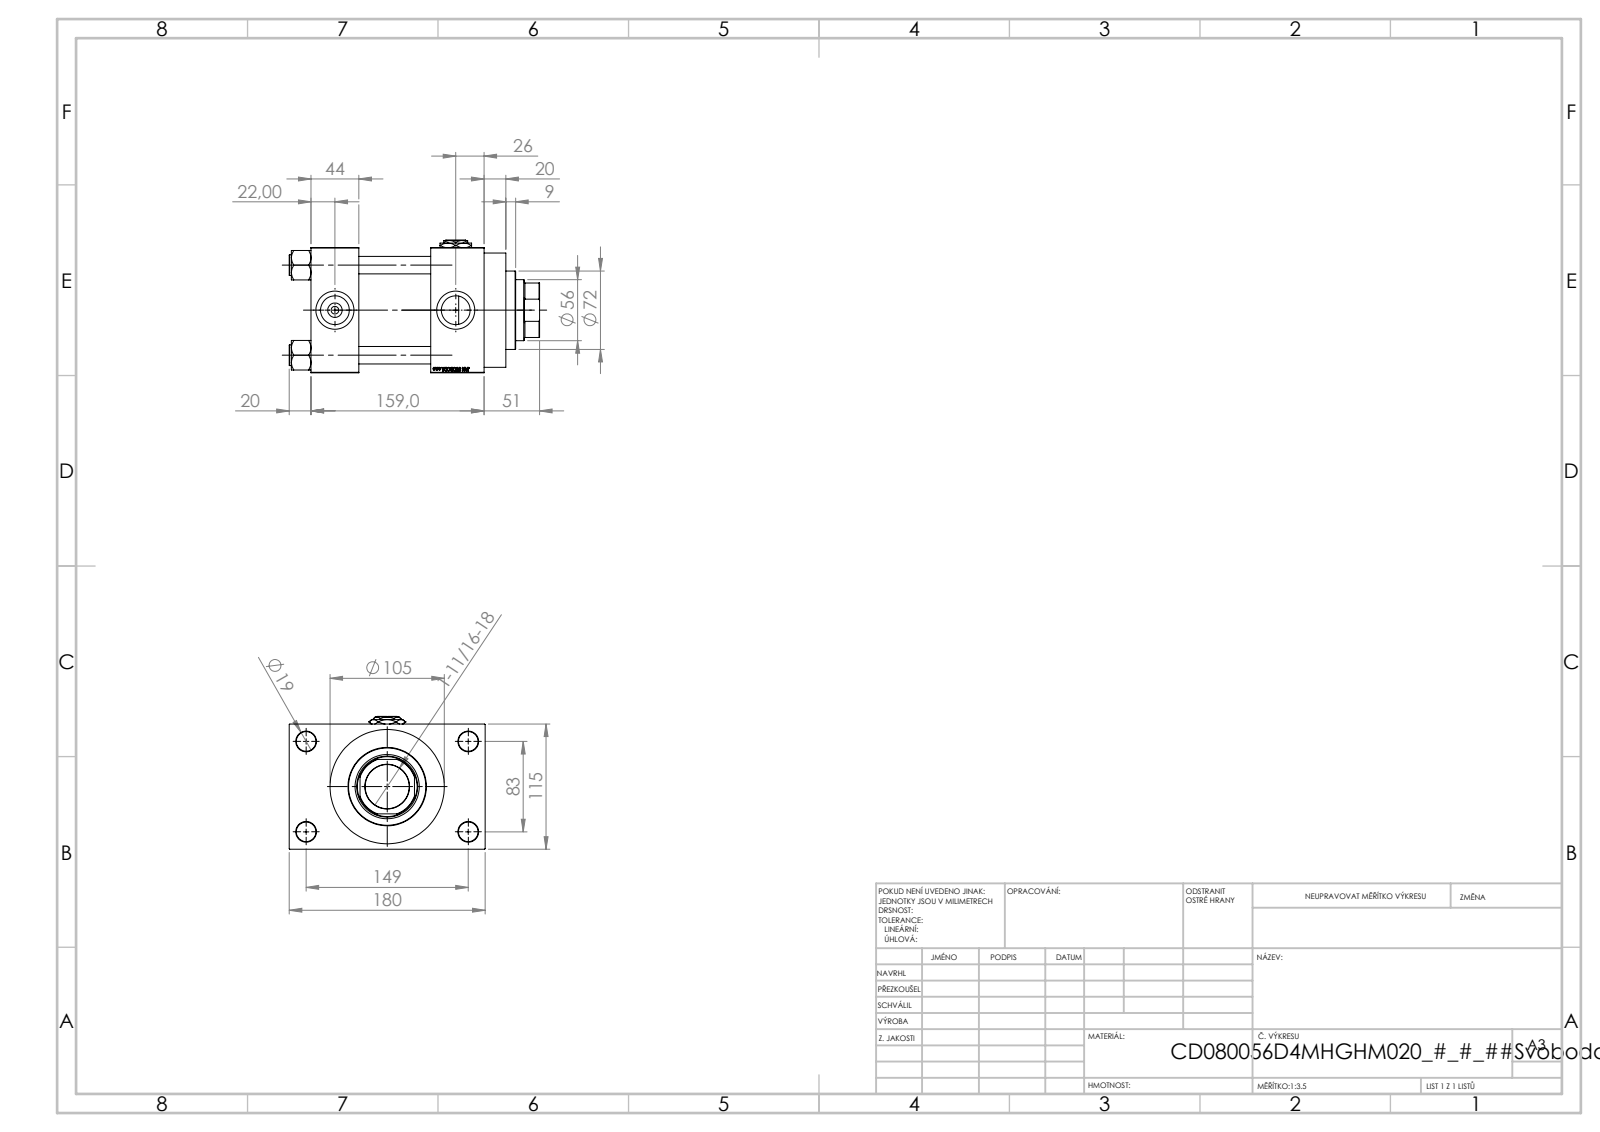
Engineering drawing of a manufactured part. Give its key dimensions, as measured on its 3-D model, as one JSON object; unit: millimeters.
{"part_name": "V215CD_NUT_M5_D; V215CD_D_TYCINKA; V215CD_VC_A; V215CD_VCP_D (+2 more)", "step_written_by": "SolidWorks 2019 (CONFIG_CONTROL_DESIGN)", "units": "millimeters", "bodies": {"solids": 12, "faces": 1196, "planar": 568, "cylindrical": 90, "other": 538}, "overall_size": [230, 180, 122], "volume_mm3": 2091000, "surface_area_mm2": 313660, "round_holes": [[16, 4], [18, 4], [26.44, 3], [35, 3], [7, 2], [40.5, 1], [56, 1], [59, 1], [61, 1], [72, 1], [80, 1]], "round_bosses_or_shafts": [[19, 4], [105, 1], [86, 1]], "partial_cylinders_radius": [[27, 1]], "face_to_face_distances": [115, 66, 110, 44, 159, 49, 32.5, 147.5, 20, 69], "hole_center_spacings": [33.15, 58.48, 82.7, 85.28, 89.24, 115.85, 142.43, 83]}
